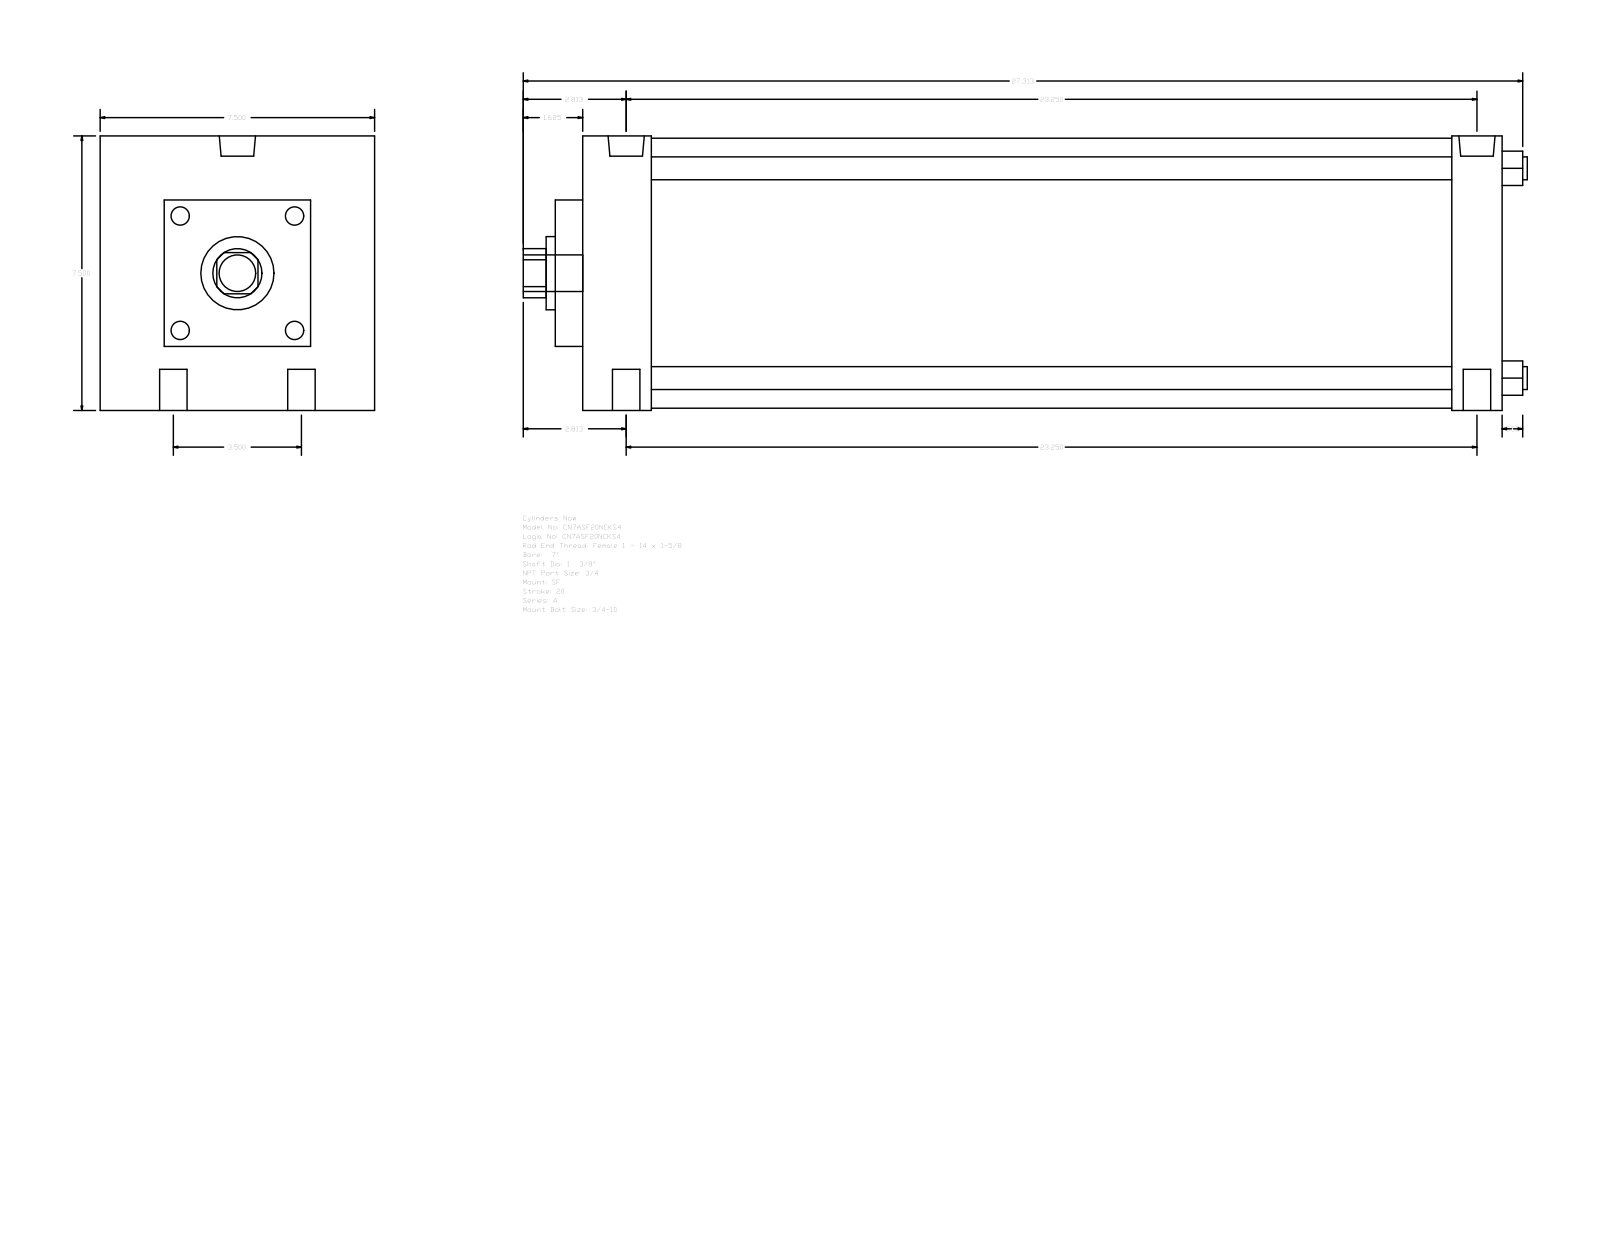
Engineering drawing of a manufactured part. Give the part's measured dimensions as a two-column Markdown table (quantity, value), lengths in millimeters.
| quantity | value |
| --- | --- |
| part name | A_SF__0700_1.375 |
| STEP written by | GSSL Pune (CONFIG_CONTROL_DESIGN) |
| units | millimeters |
| bodies | 0 solids, 93 faces (67 planar, 26 cylindrical, 0 other) |
| overall size | 696.91 × 190.5 × 190.5 |
| round holes (diameter × count) | 19.05 × 4, 15.08 × 2, 25.12 × 2, 34.92 × 1, 50.8 × 1 |
| round bosses / shafts (diameter × count) | 15.88 × 4, 187.32 × 1, 25.4 × 1 |
| partial cylindrical surfaces (radius × count) | 17.06 × 1 |
| main face-to-face distances | 190.5, 638.18, 19.04, 657.22, 66.67, 622.29, 47.63, 603.25, 555.62, 590.55 |
| hole center spacings | 44.45, 592.22, 590.55, 88.9, 597.2, 579.43 |
